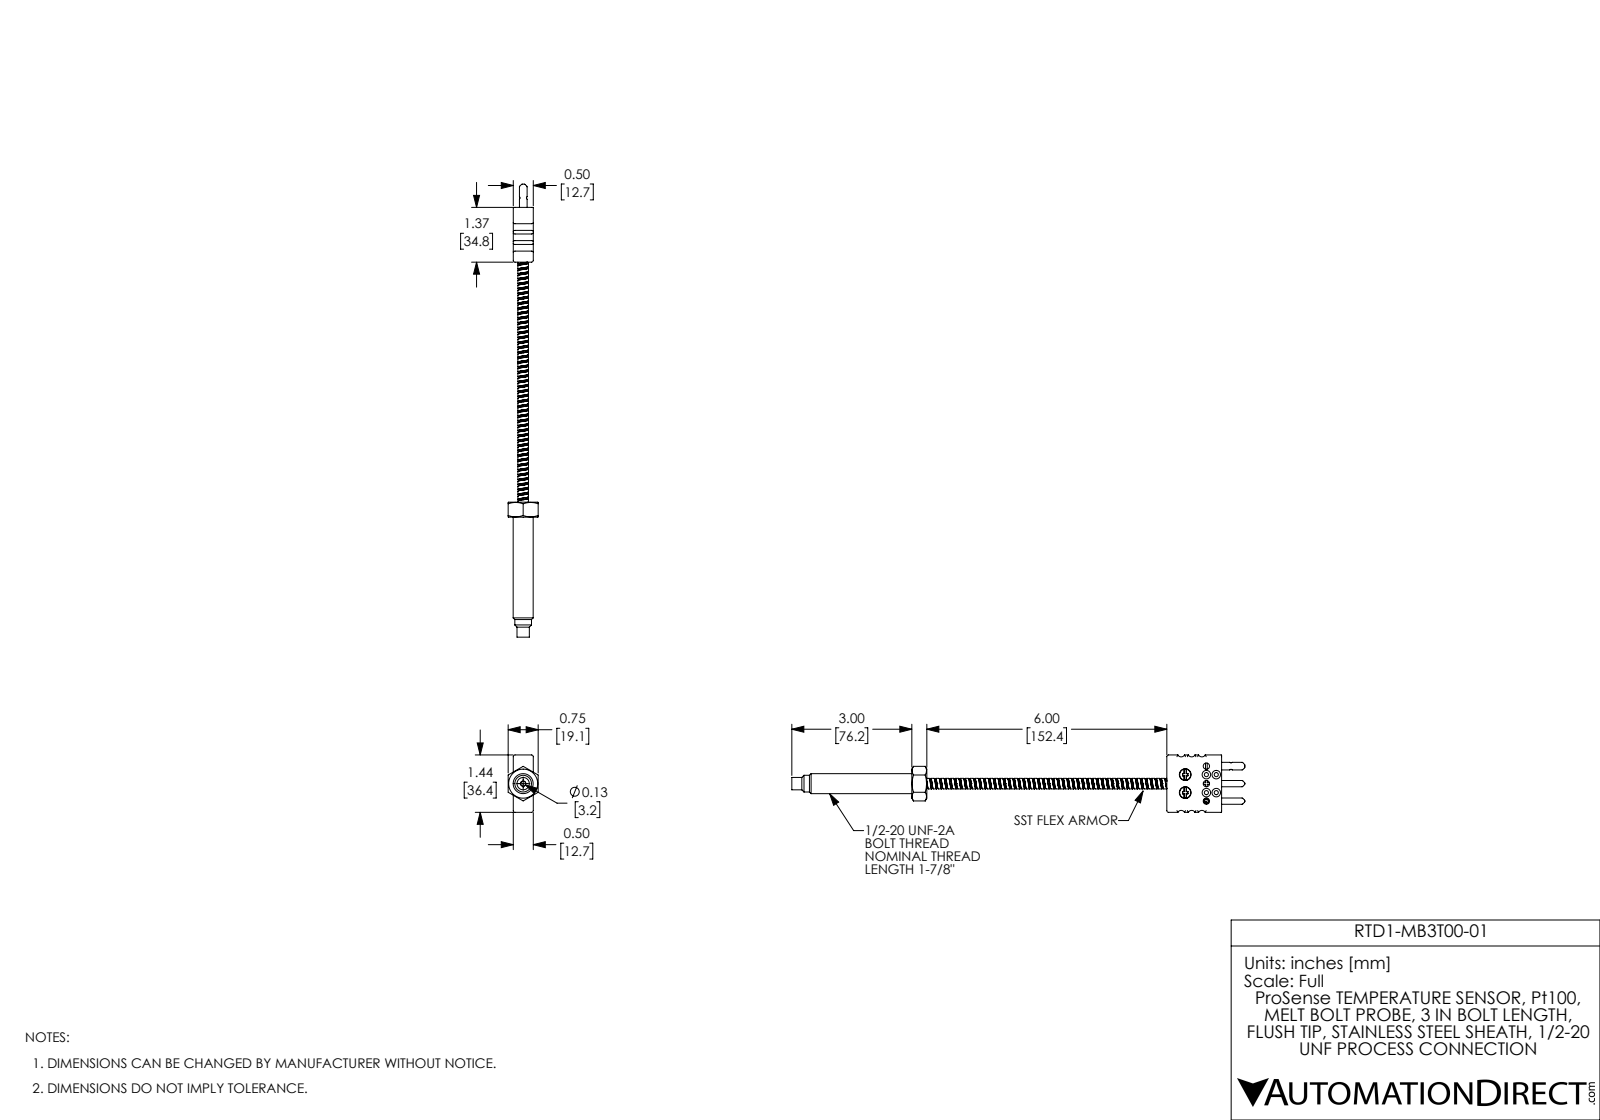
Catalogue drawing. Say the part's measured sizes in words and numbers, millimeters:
The part is named "RTD1-MB3T00-01". Its 3-D file was written by "SolidWorks 2017 (AUTOMOTIVE_DESIGN)". It is 3 solids with 412 faces: 106 planar, 190 cylindrical and 116 other. Overall it measures 287.7 by 36.4 by 19.1 millimeters. Its volume is 32 410 cubic millimeters and its surface area 14 030 square millimeters. Round holes: 4 of diameter 2.6, 3 of diameter 4, 2 of diameter 4.7, 2 of diameter 7.5, 1 of diameter 3.4, 1 of diameter 7.8. Round bosses or shafts: 2 of diameter 7.1, 2 of diameter 4, 2 of diameter 2.6, 1 of diameter 12.7, 1 of diameter 10.6, 1 of diameter 7.8, 1 of diameter 6.7, 1 of diameter 4.9. Partial cylindrical surfaces (rounded edges, fillets, slot ends): 8 of radius 1.1, 6 of radius 2.4, 4 of radius 0.3. The main face-to-face distances are 12.7, 34.8, 19.1, 187.2, 152.4, 36.4, 196.7, 161.9, 9.5, 15.8. The hole center spacings are 13.4, 14.5, 19.7, 5.4, 5.7, 6.3, 8.3, 8.5.
